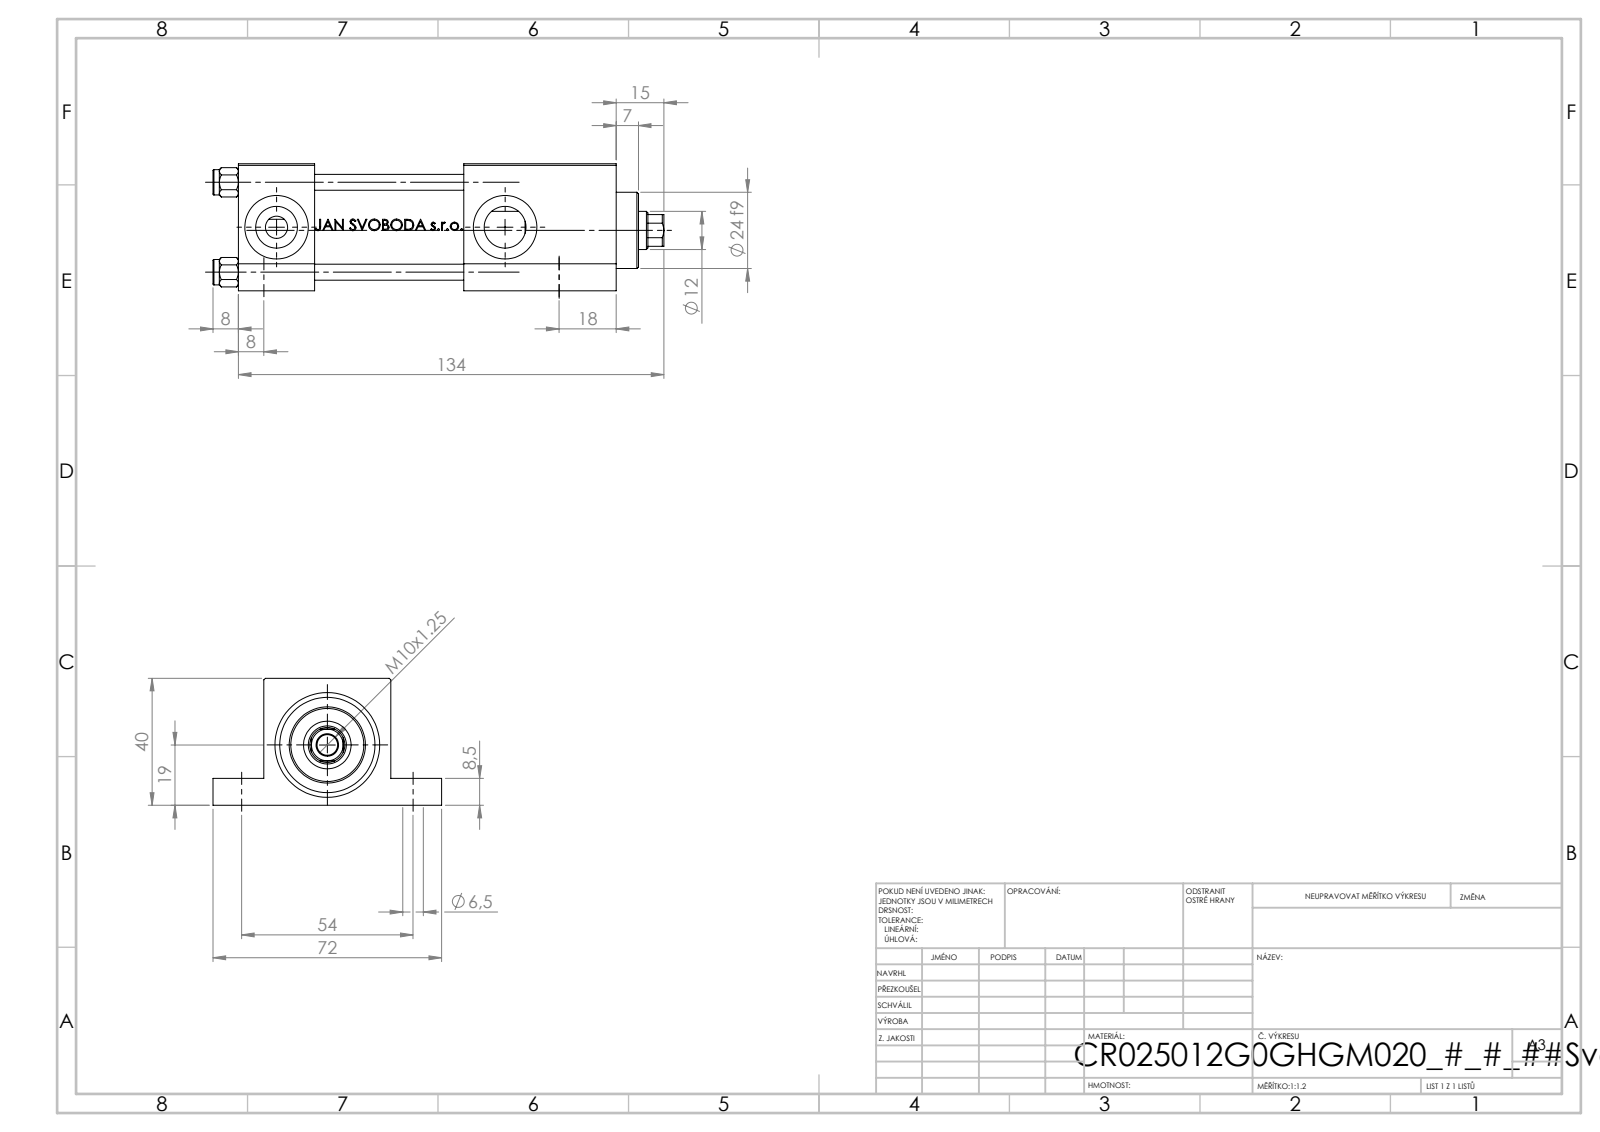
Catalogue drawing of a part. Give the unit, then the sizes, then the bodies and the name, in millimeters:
Units: millimetres
Overall size (bounding box): 142 × 72 × 40
Round holes (diameter × count): ⌀6.5 ×5, ⌀5 ×4, ⌀20 ×3, ⌀7 ×2, ⌀13.16 ×2, ⌀12 ×1, ⌀15 ×1, ⌀25 ×1, ⌀30 ×1
Round bosses / shafts (diameter × count): ⌀8 ×4, ⌀31 ×1, ⌀24 ×1
Partial cylindrical surfaces — rounded edges, fillets, slot ends (radius × count): R5.5 ×1
Main face-to-face distances: 40, 8.5, 31.5, 24, 119, 95, 16, 56, 48, 71
Hole centre spacings: 28.3, 19.32, 20.73, 40.02, 54, 93, 107.54, 72
Volume: 161 747 mm³ · Surface area: 59 769 mm²
Bodies: 11 solids, 1086 faces (430 planar, 124 cylindrical, 532 other)
Part name (STEP PRODUCT): V215CR_G_TYCINKA; V215CR_G_Body; NUT_M5_G; V215_VC_A (+1 more)
STEP written by: SolidWorks 2019 (CONFIG_CONTROL_DESIGN)
